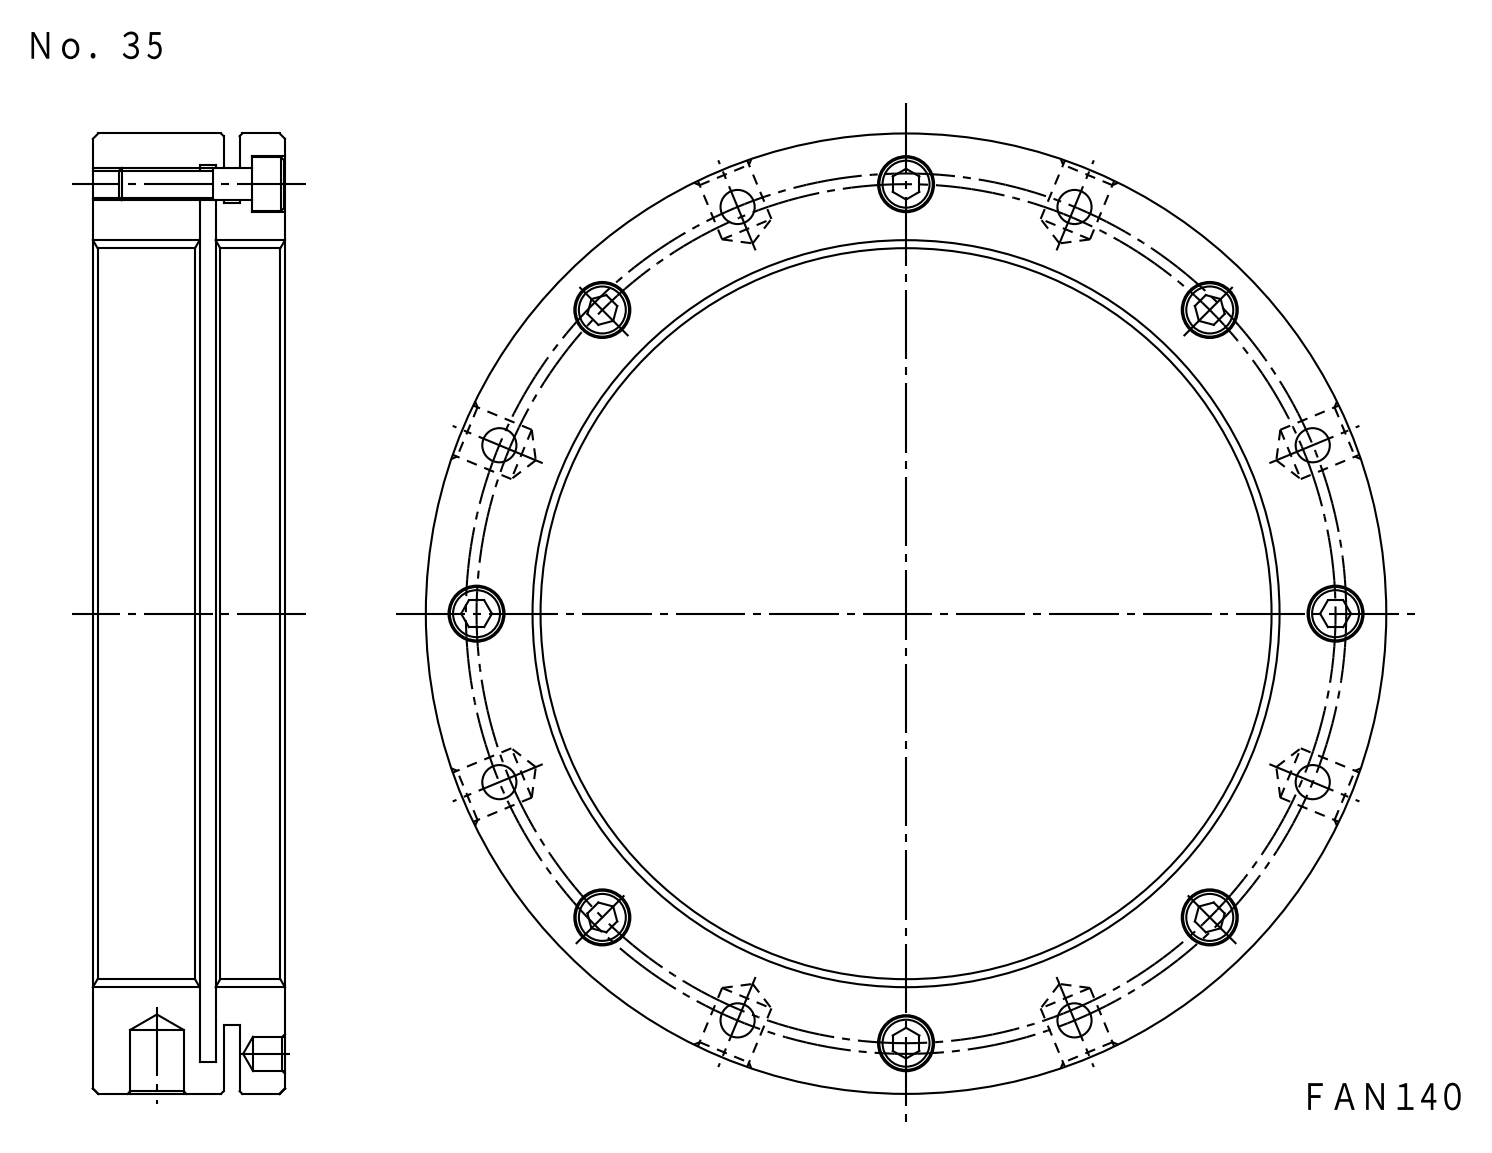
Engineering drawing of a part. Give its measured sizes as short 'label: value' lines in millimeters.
name: FKD FAN140; M6X25_default
written by: SolidWorks 2012 (CONFIG_CONTROL_DESIGN)
unit: mm
bodies: 9 solids, 266 faces (94 planar, 140 cylindrical, 32 other)
size: 180 × 180 × 36
volume: 311 370 mm³; area: 97 923 mm²
holes: 8× ⌀6.4, 8× ⌀6.8, 8× ⌀10, 8× ⌀11, 6× ⌀4.92, 2× ⌀4.92, 1× ⌀140, 1× ⌀168
bosses: 8× ⌀10, 8× ⌀6, 1× ⌀180, 1× ⌀154
face distances: 3, 4.5, 36, 20, 16, 24.5, 11.5, 27.5, 7.5, 8.5
hole spacings: 31.86, 90.57, 135.53, 61.61, 63.14, 80.5, 82.5, 113.84
